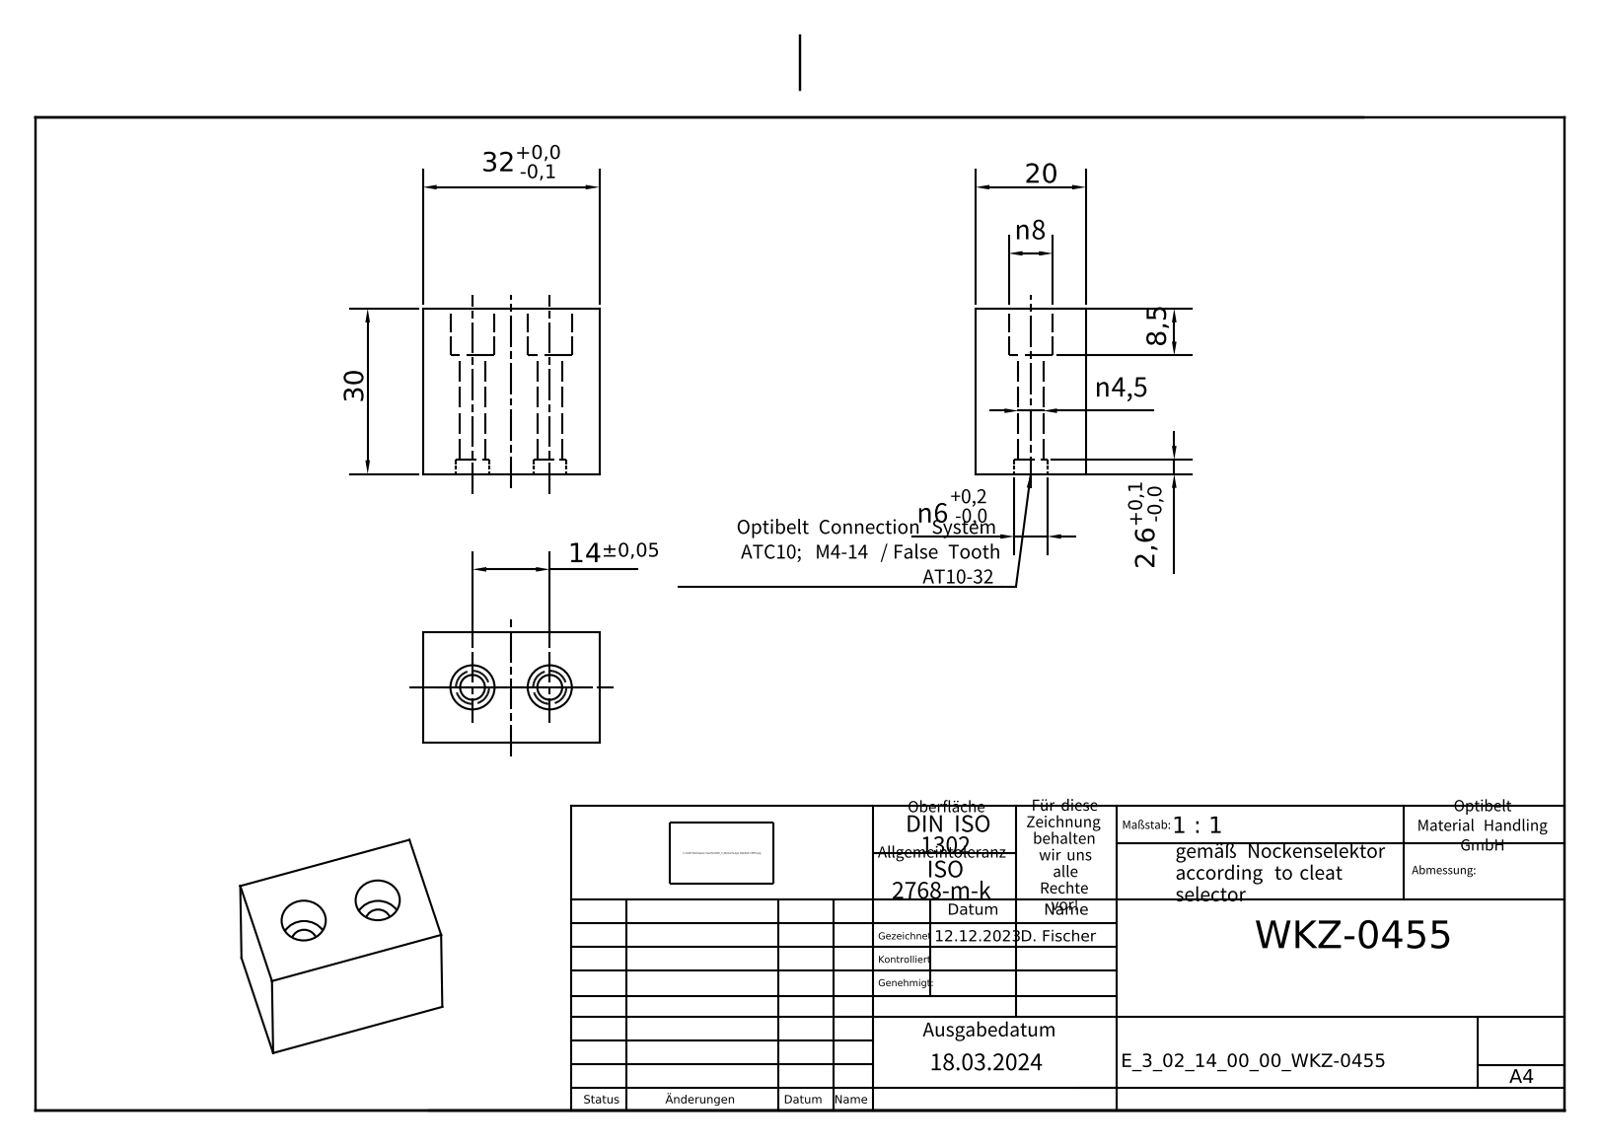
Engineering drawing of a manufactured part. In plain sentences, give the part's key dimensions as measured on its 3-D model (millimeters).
The part is named "E_3_02_14_00_00_WKZ-0455". Its 3-D file was written by "Autodesk Inventor 2025 (AUTOMOTIVE_DESIGN)". It is 1 solid with 16 faces: 10 planar, 6 cylindrical and 0 other. Overall it measures 32 by 30 by 20 millimeters. Its volume is 17 597 cubic millimeters and its surface area 5 396 square millimeters. Round holes: 2 of diameter 4.5, 2 of diameter 6, 2 of diameter 8. The main face-to-face distances are 20, 32, 30, 21.5, 8.5, 2.6, 18.9, 27.4. The hole center spacings are 14.
